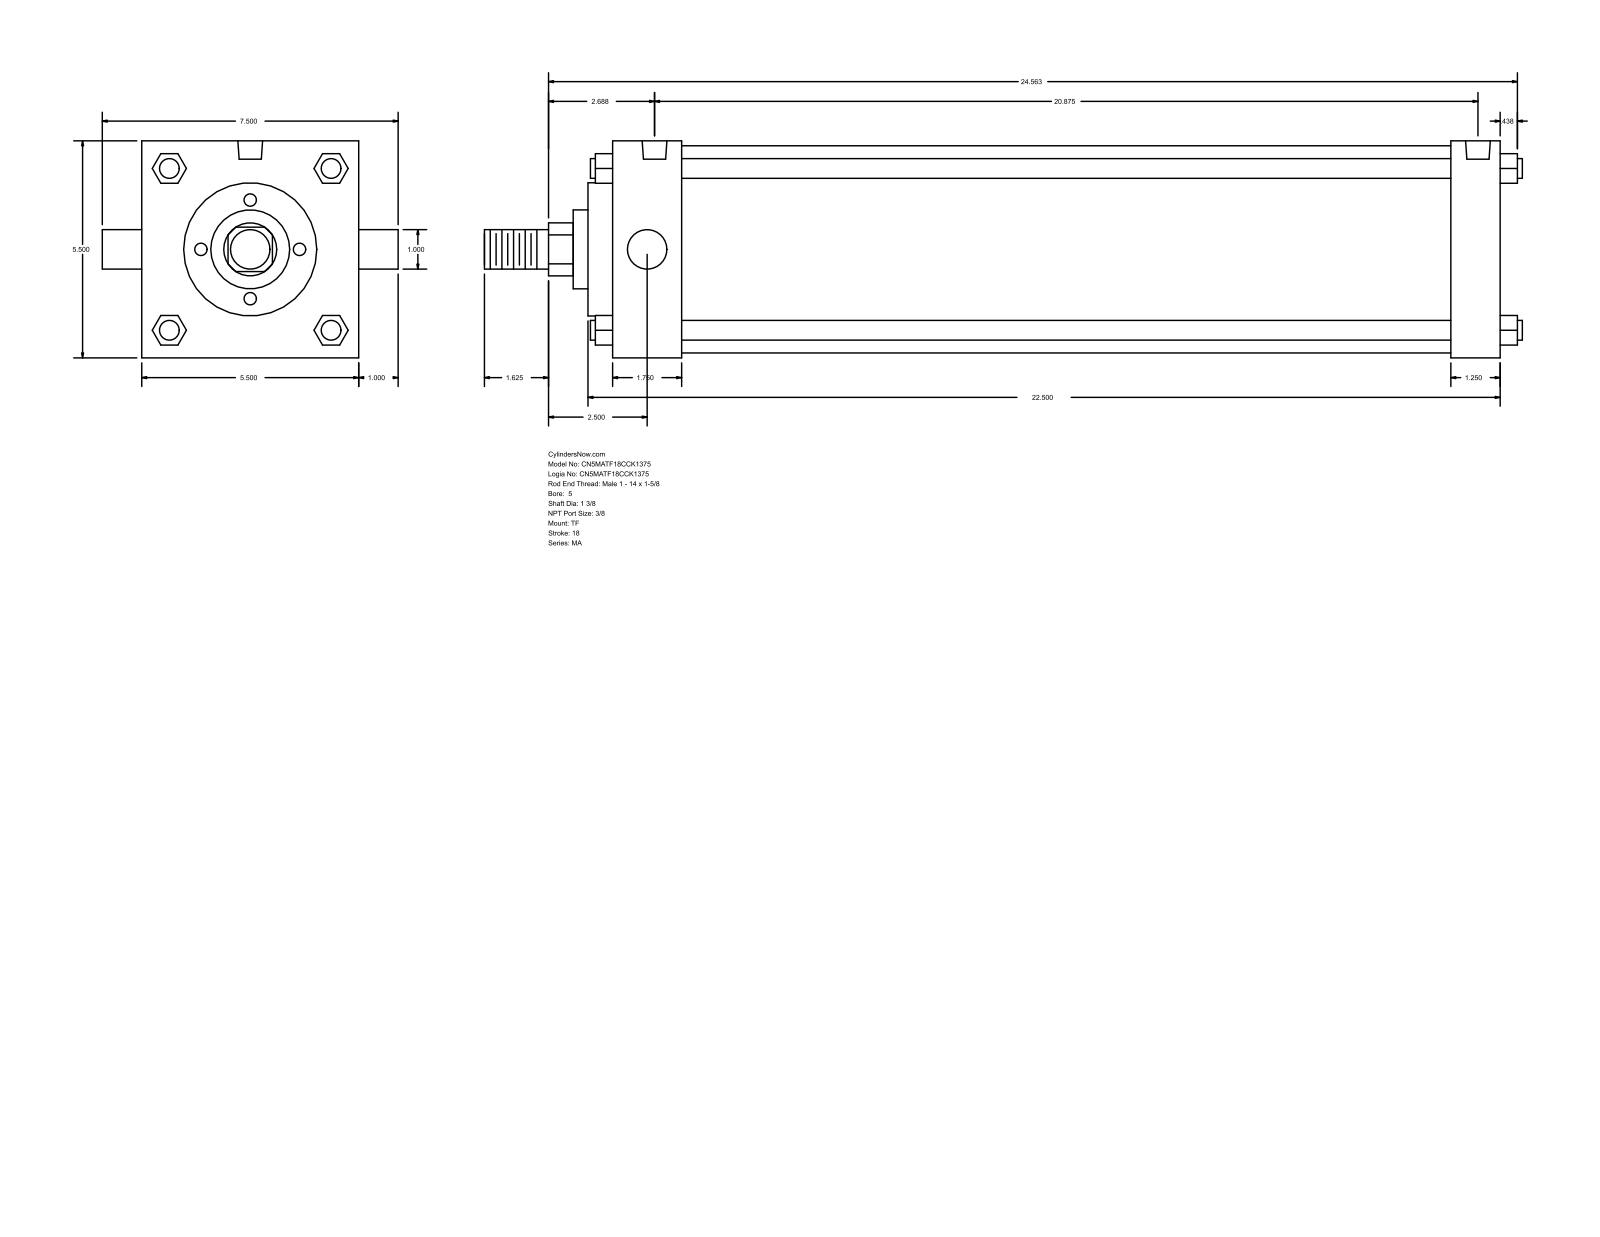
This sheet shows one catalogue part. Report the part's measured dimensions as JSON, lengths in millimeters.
{"part_name": "MA_TF__0500_1.375", "step_written_by": "GSSL Pune (CONFIG_CONTROL_DESIGN)", "units": "millimeters", "bodies": {"solids": 0, "faces": 122, "planar": 93, "cylindrical": 29, "other": 0}, "overall_size": [668.34, 190.5, 139.7], "round_holes": [[11.11, 3], [15.93, 2]], "round_bosses_or_shafts": [[12.7, 4], [25.4, 2], [133.35, 1], [85.72, 1], [50.8, 1], [34.92, 1]], "partial_cylinders_radius": [[17.06, 1]], "face_to_face_distances": [139.7, 571.5, 539.75, 31.75, 44.45, 495.3, 527.05, 15.87, 60.32, 555.62], "hole_center_spacings": [4.76, 4.77, 520.7, 525.46, 525.47, 530.23]}
